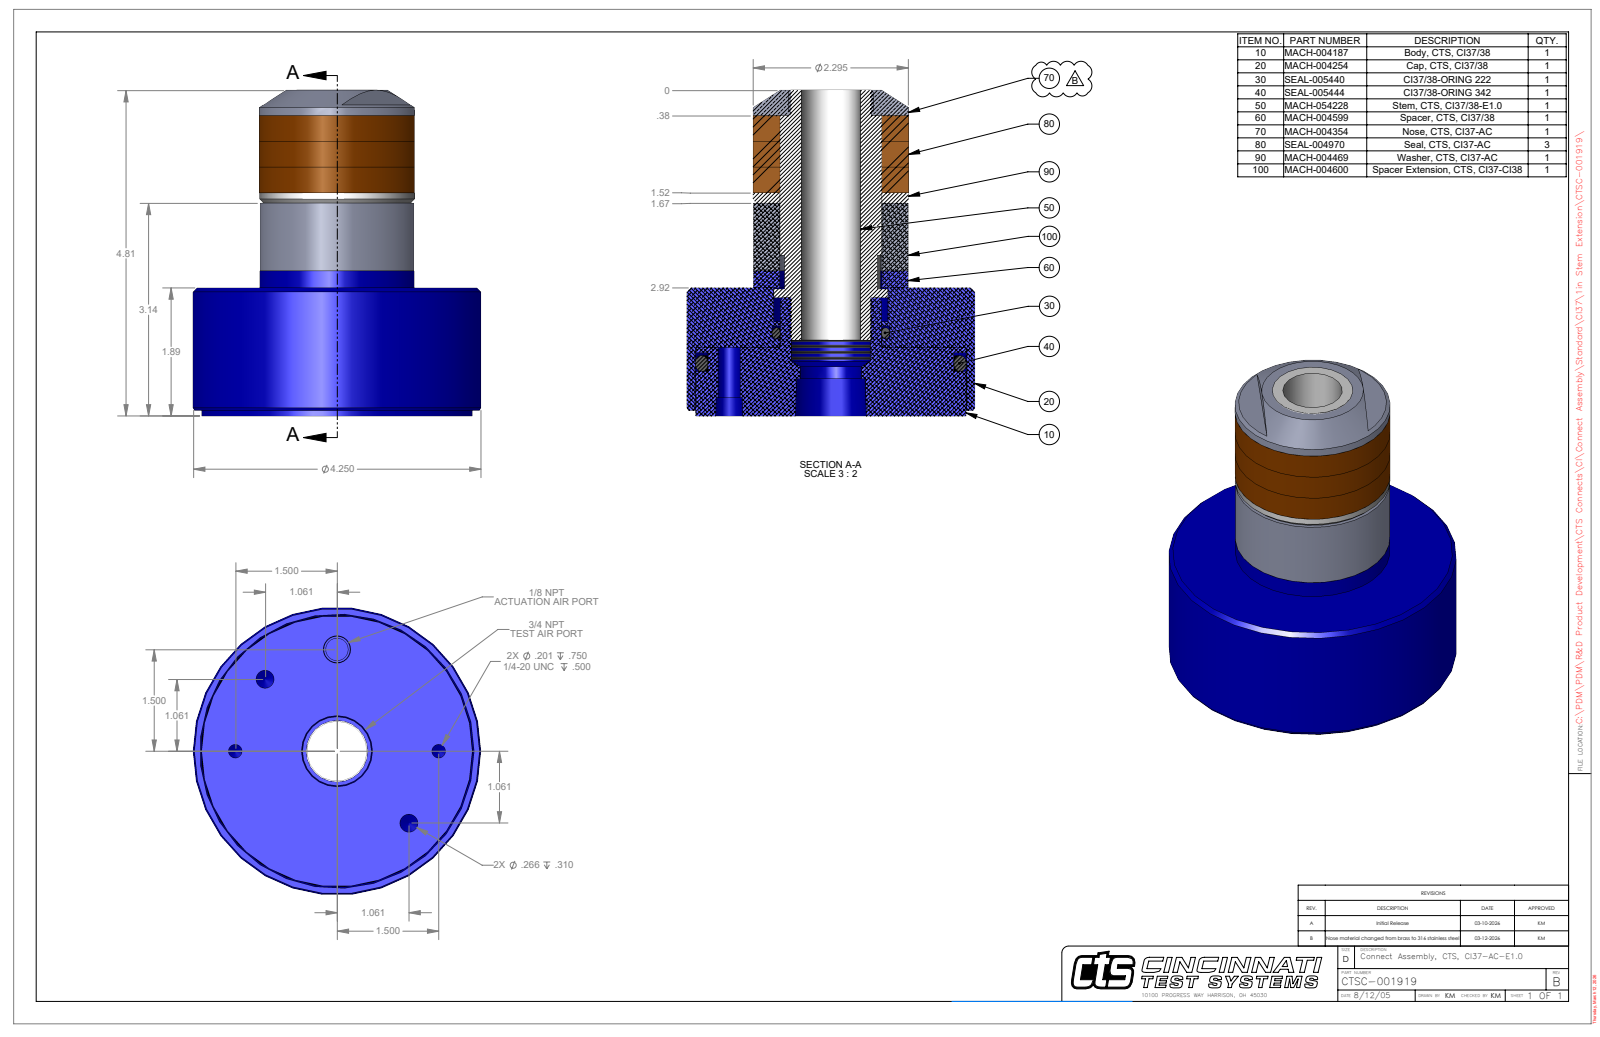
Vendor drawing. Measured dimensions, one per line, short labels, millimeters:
name: CTSC-001919
written by: SolidWorks 2023 (AUTOMOTIVE_DESIGN)
unit: mm
bodies: 8 solids, 78 faces (37 planar, 28 cylindrical, 13 other)
size: 122.25 × 107.95 × 107.95
volume: 573 039 mm³; area: 96 841 mm²
holes: 2× ⌀5.11, 2× ⌀6.75, 1× ⌀22.35, 1× ⌀23.01, 1× ⌀29.77, 1× ⌀37.97, 1× ⌀38.35, 1× ⌀42.88, 1× ⌀101.6
bosses: 1× ⌀107.95, 1× ⌀101.4, 1× ⌀58.29, 1× ⌀58.29, 1× ⌀57.94, 1× ⌀42.52, 1× ⌀38.05, 1× ⌀31.75
face distances: 48.08, 9.65, 19.31, 112.65, 64.57, 93.34, 103, 45.26, 54.92, 9.66
hole spacings: 38.1, 29.16, 70.4, 76.2
